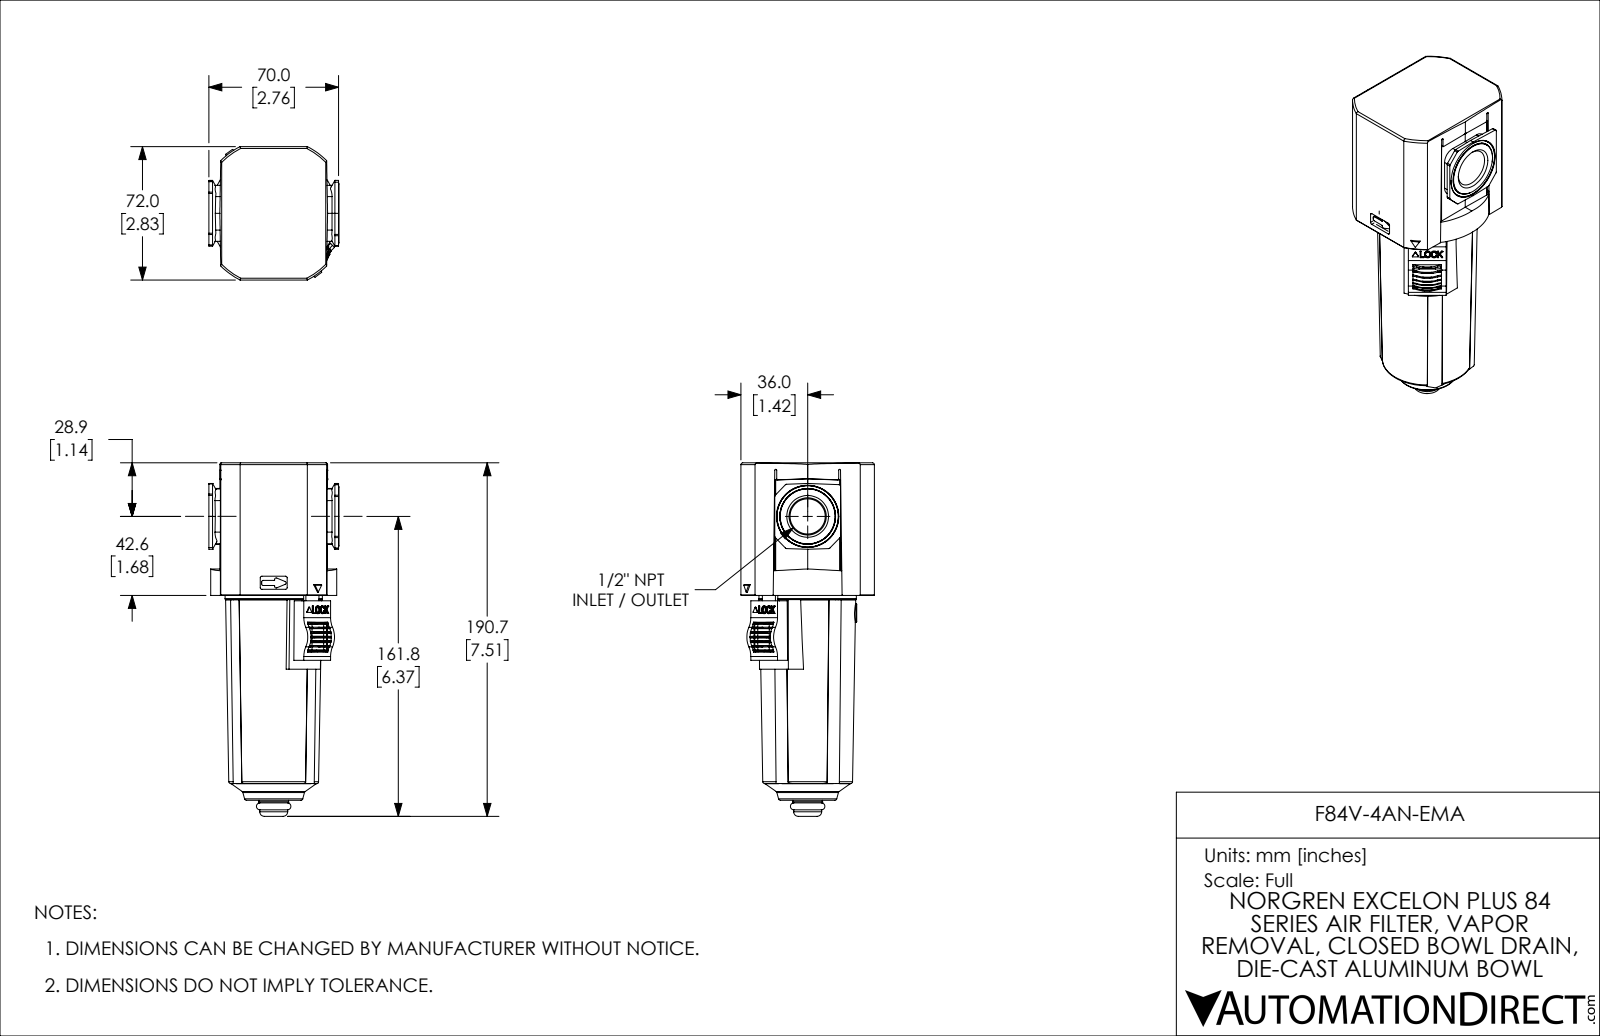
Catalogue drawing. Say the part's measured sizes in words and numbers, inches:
The part is named "F84V-4AN-EMA". Its 3-D file was written by "SolidWorks 2021 (CONFIG_CONTROL_DESIGN)". It is 5 solids with 998 faces: 416 planar, 364 cylindrical and 218 other. Overall it measures 7.508 by 2.835 by 2.766 inches. Its volume is 26.9 cubic inches and its surface area 148 square inches. Round holes: 2 of diameter 0.163, 1 of diameter 0.126, 1 of diameter 0.268, 1 of diameter 0.633, 1 of diameter 2.461. Round bosses or shafts: 2 of diameter 0.315, 2 of diameter 0.276, 1 of diameter 2.122, 1 of diameter 2.067, 1 of diameter 2.018, 1 of diameter 1.959, 1 of diameter 1.953, 1 of diameter 0.906. Partial cylindrical surfaces (rounded edges, fillets, slot ends): 46 of radius 0.039, 37 of radius 0.02, 16 of radius 0.028, 14 of radius 0.01, 8 of radius 0.008, 8 of radius 0.038, 8 of radius 0.045, 8 of radius 0.06. The main face-to-face distances are 0.059, 2.411, 2.352, 2.047, 2.835, 1.988, 0.364, 2.756, 0.404, 0.768. The hole center spacings are 0.594, 1.189.
